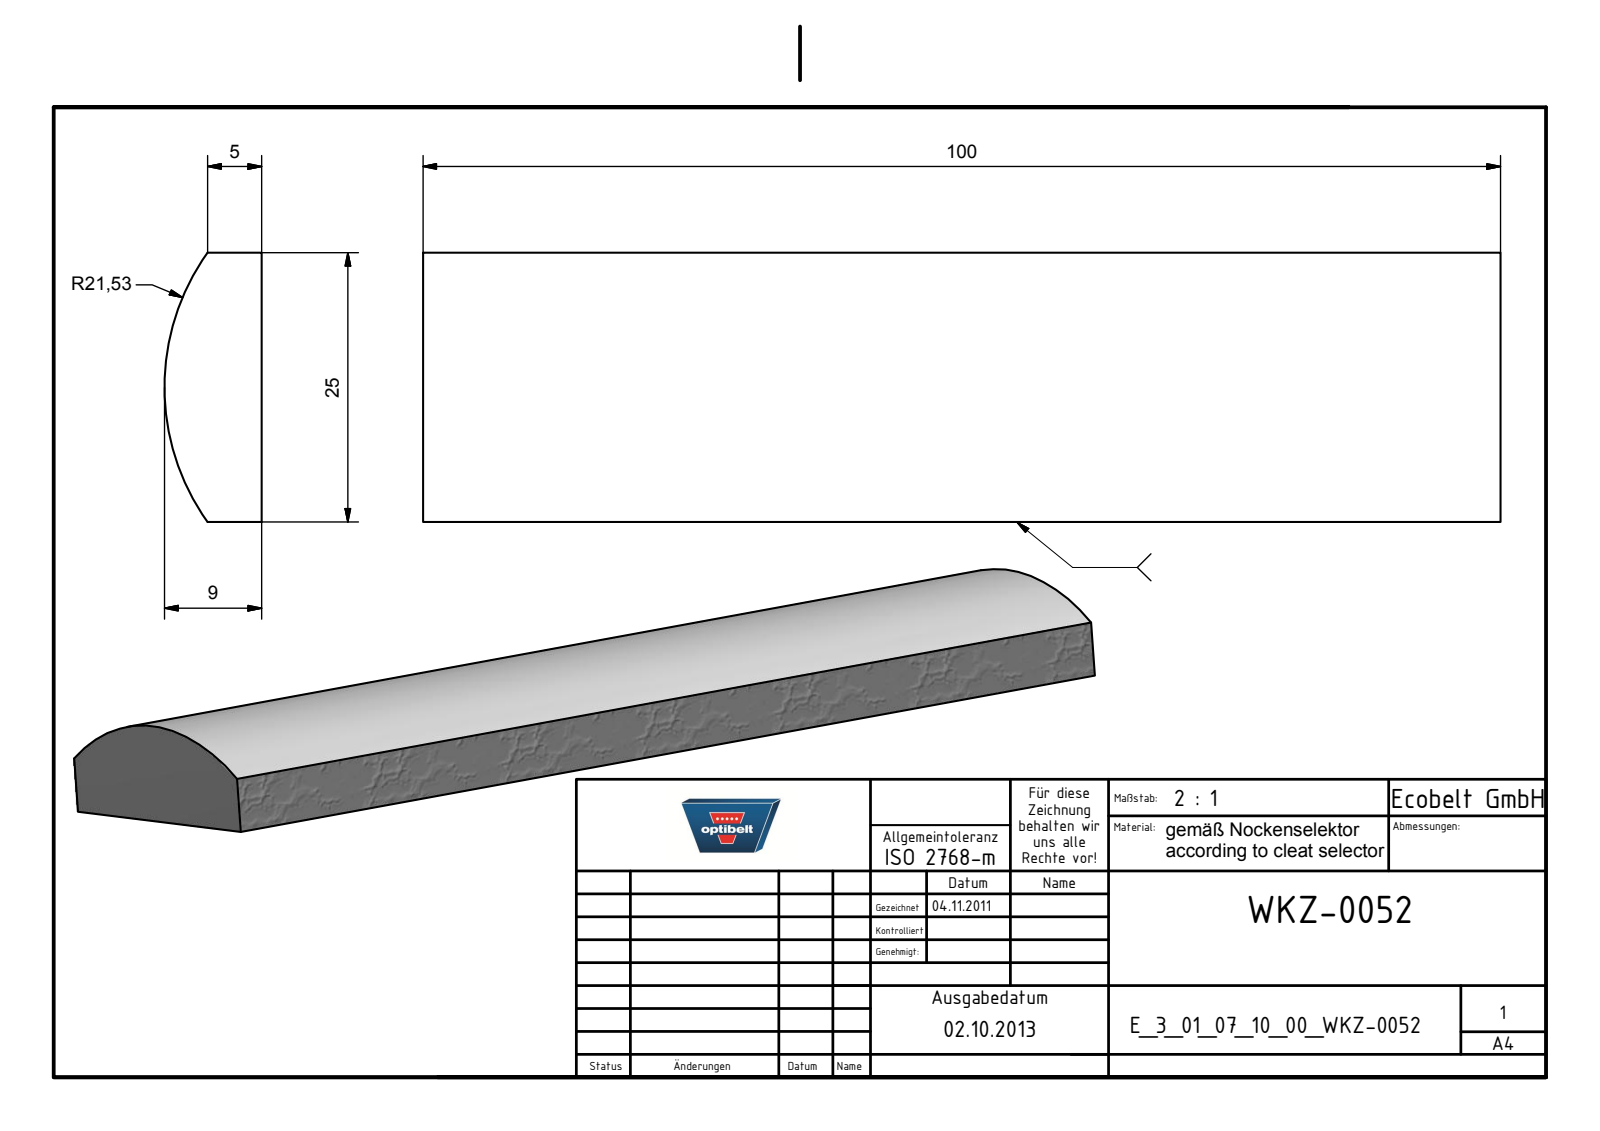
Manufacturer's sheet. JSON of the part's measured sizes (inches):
{"part_name": "E_3_01_07_10_00_WKZ-0052", "step_written_by": "Autodesk Inventor 2025 (AUTOMOTIVE_DESIGN)", "units": "inches", "bodies": {"solids": 1, "faces": 6, "planar": 5, "cylindrical": 1, "other": 0}, "overall_size": [3.937, 0.984, 0.354], "volume_in3": 1.178, "surface_area_in2": 10.16, "partial_cylinders_radius": [[0.848, 1]], "face_to_face_distances": [0.984, 3.937]}
